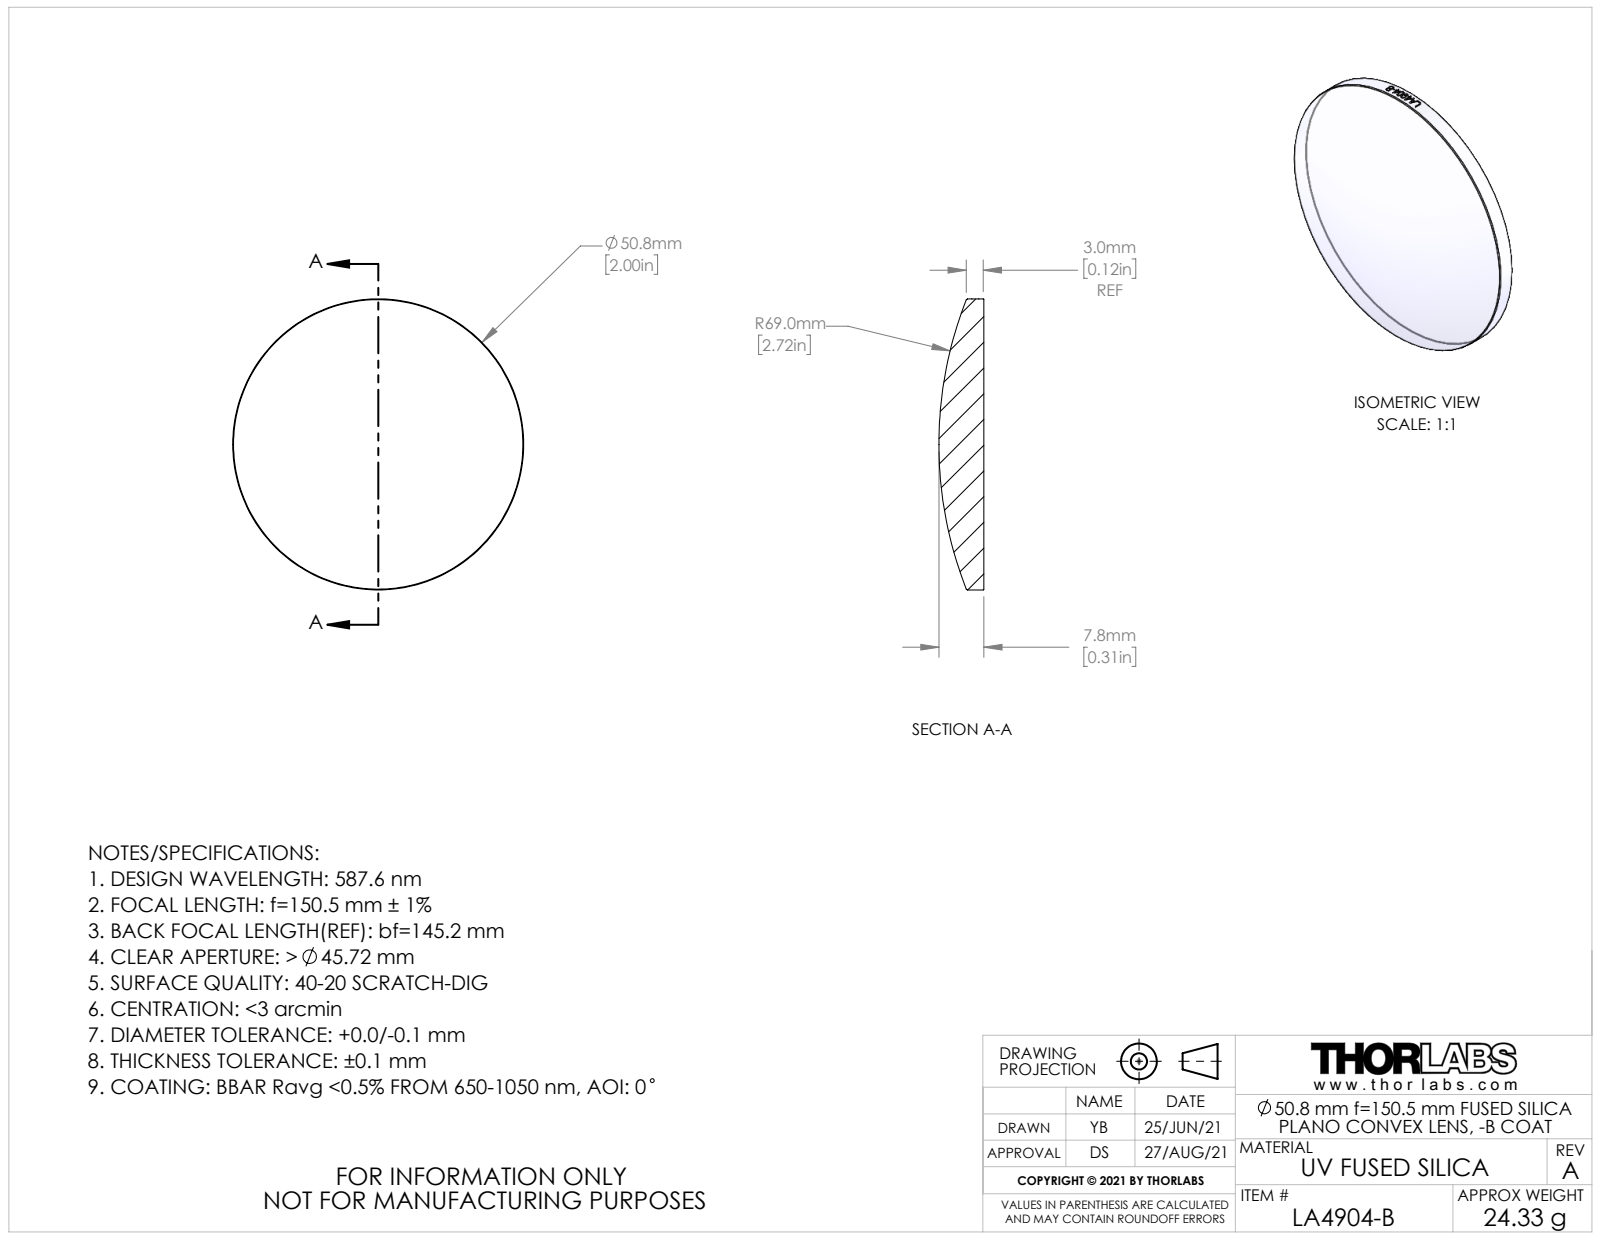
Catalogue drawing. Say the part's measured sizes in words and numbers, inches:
The part is named "CTN017905-E0W". Its 3-D file was written by "SolidWorks 2018 (AUTOMOTIVE_DESIGN)". It is 1 solid with 24 faces: 1 planar, 17 cylindrical and 6 other. Overall it measures 2 by 2 by 0.309 inches. Its volume is 0.674 cubic inches and its surface area 7.111 square inches. Round bosses or shafts: 1 of diameter 2.
